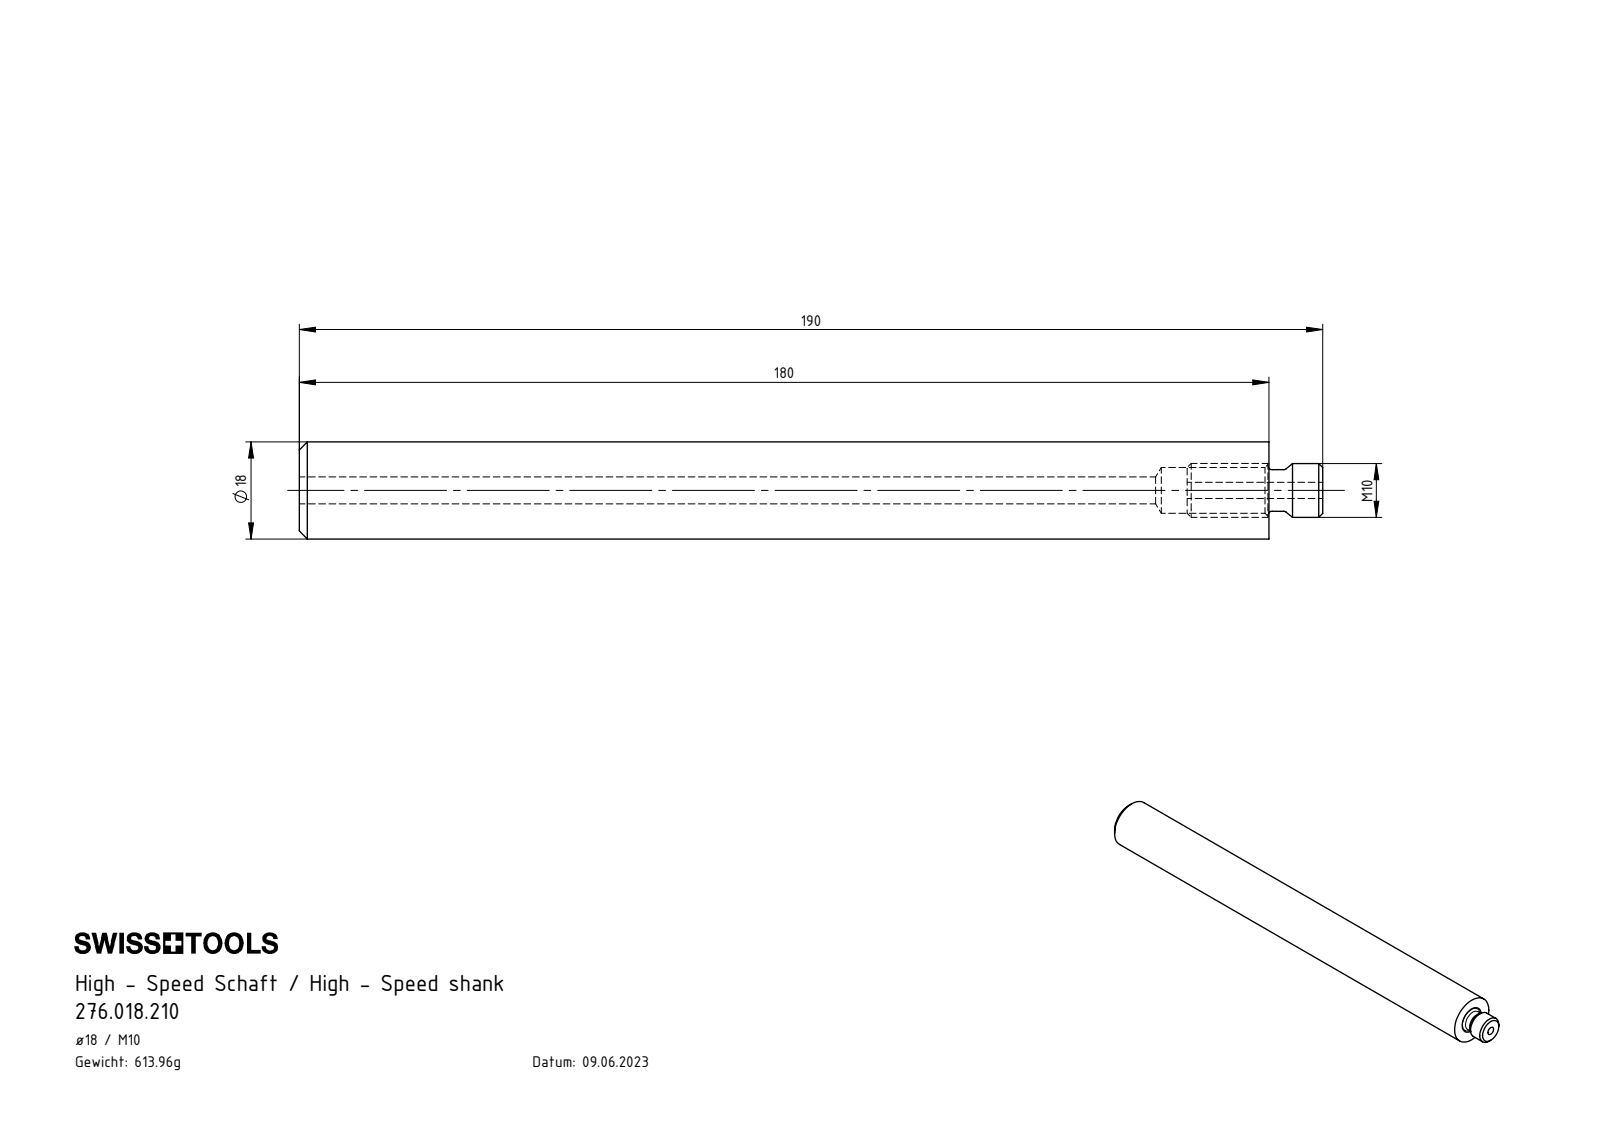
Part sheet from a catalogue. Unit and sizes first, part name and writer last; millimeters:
Units: millimetres
Overall size (bounding box): 190 × 18 × 18
Round holes (diameter × count): ⌀3 ×1, ⌀5 ×1, ⌀8.5 ×1
Round bosses / shafts (diameter × count): ⌀18 ×1, ⌀10 ×1, ⌀7.7 ×1
Main face-to-face distances: 180, 190, 10, 164.8, 15.2, 25.2, 179.8, 15, 10.2
Volume: 43 105 mm³ · Surface area: 14 772 mm²
Bodies: 2 solids, 35 faces (5 planar, 14 cylindrical, 16 other)
Part name (STEP PRODUCT): U18-HS0.K01.180_A; HM1-U18.001.180_A; HM1-BG1.010.025_A
STEP written by: SolidWorks 2017 (AUTOMOTIVE_DESIGN)
